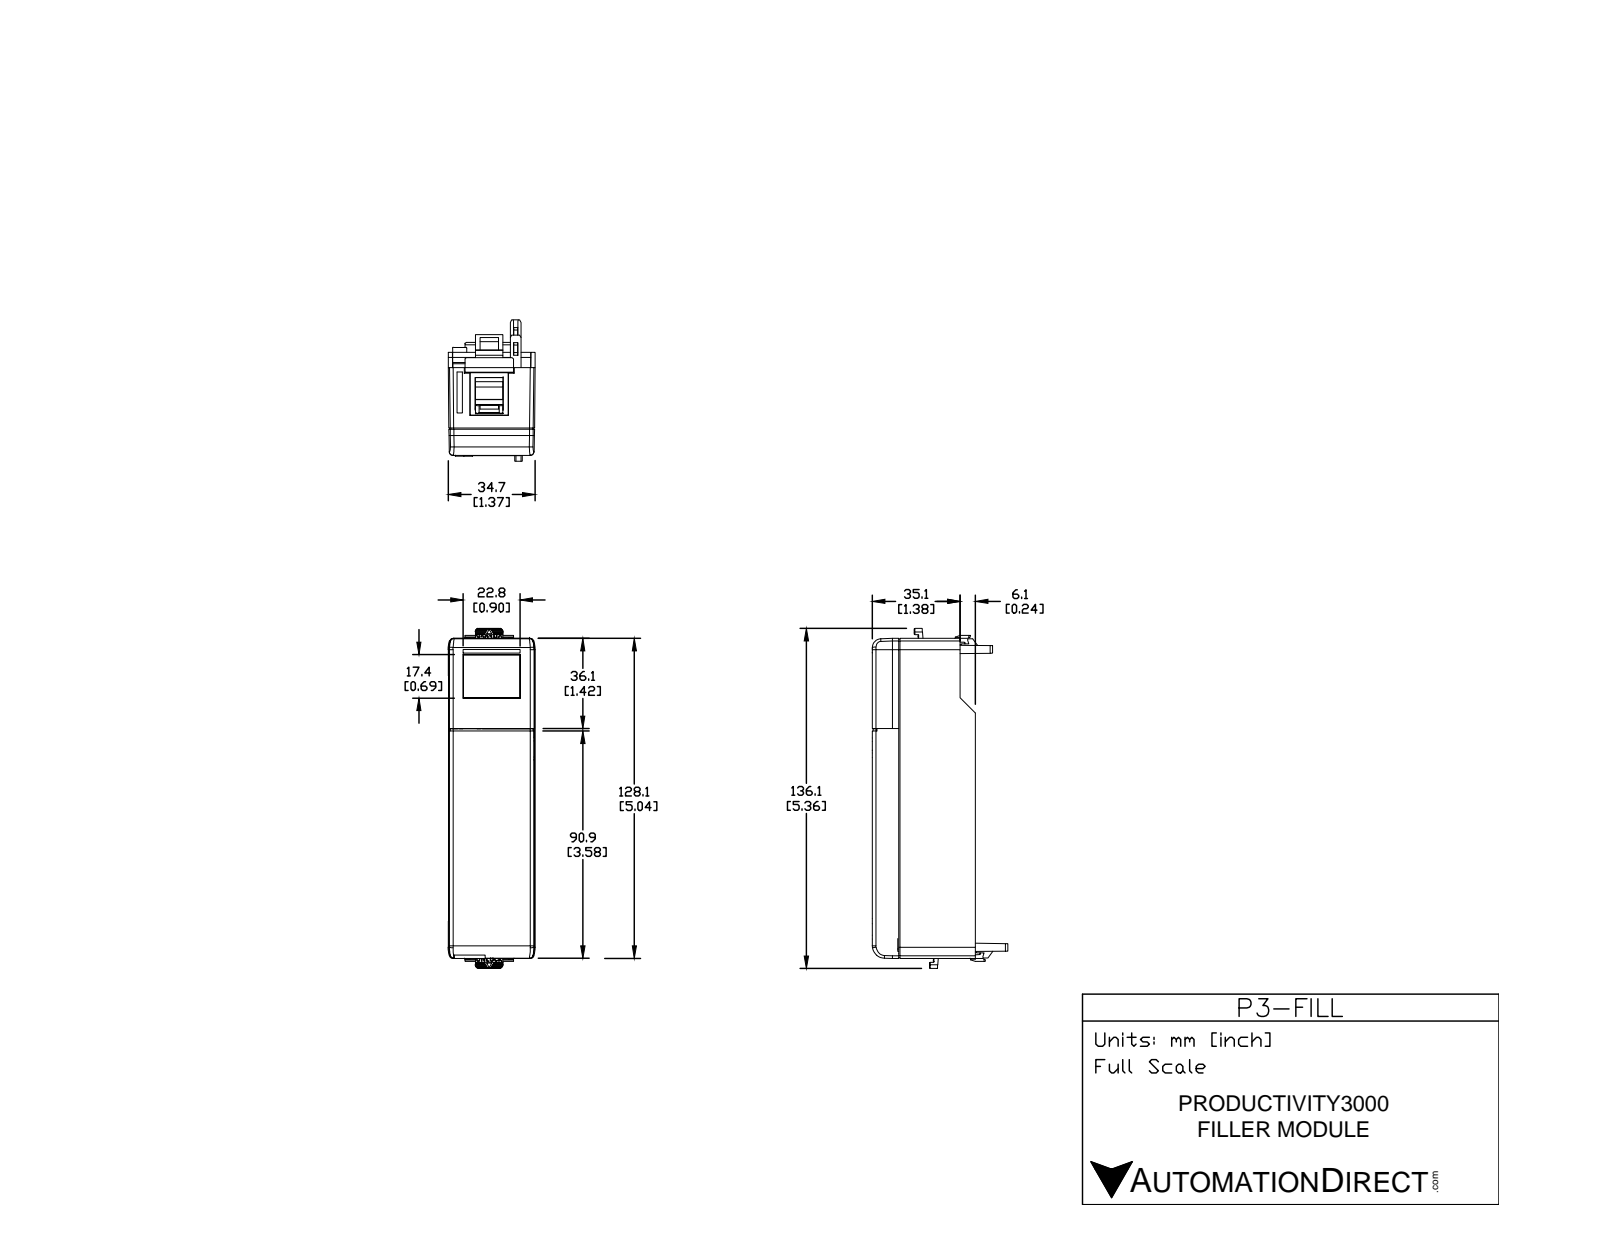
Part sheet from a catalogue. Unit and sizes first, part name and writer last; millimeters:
Units: millimetres
Overall size (bounding box): 140.28 × 54.28 × 34.8
Partial cylindrical surfaces — rounded edges, fillets, slot ends (radius × count): R1 ×6, R1.5 ×6, R0.3 ×4, R0.8 ×4, R0.5 ×3, R1.15 ×2, R1.2 ×2, R2.3 ×2
Main face-to-face distances: 41.23, 0.9, 1.7, 0.8, 40.43, 39.53, 6.1, 33.43, 34.33, 35.13
Volume: 173 994 mm³ · Surface area: 29 230 mm²
Bodies: 1 solid, 886 faces (819 planar, 37 cylindrical, 30 other)
Part name (STEP PRODUCT): P3-FILL
STEP written by: SolidWorks 2009 (CONFIG_CONTROL_DESIGN)
